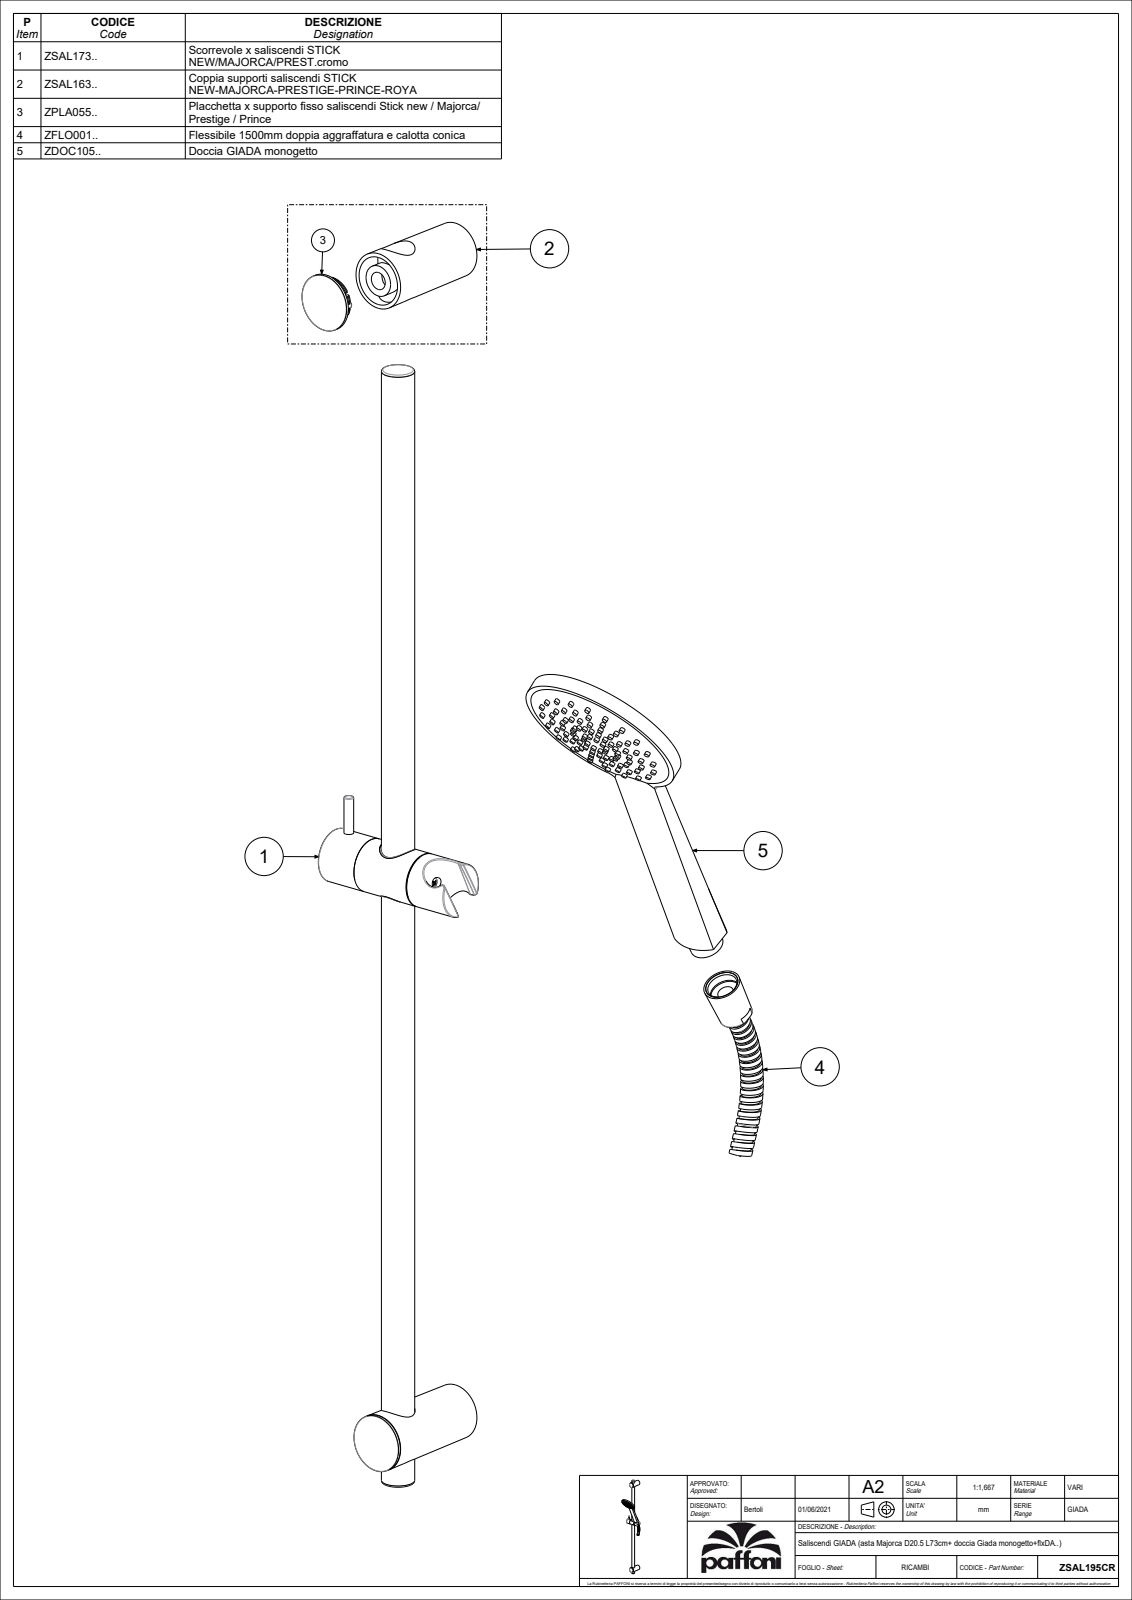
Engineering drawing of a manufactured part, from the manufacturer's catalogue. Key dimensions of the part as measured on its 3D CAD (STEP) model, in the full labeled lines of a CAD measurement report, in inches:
Part name (STEP PRODUCT): ZSAL195CR
STEP written by: CREO PARAMETRIC BY PTC INC, 2020044 (CONFIG_CONTROL_DESIGN)
Units: inches
Bodies: 5 solids, 769 faces (161 planar, 347 cylindrical, 261 other)
Overall size (bounding box): 28.898 × 7.874 × 5.693
Volume: 36.75 in³ · Surface area: 277.4 in²
Round holes (diameter × count): ⌀1.22 ×3, ⌀0.213 ×2, ⌀0.441 ×2, ⌀0.886 ×2, ⌀0.15 ×1, ⌀0.315 ×1, ⌀0.433 ×1, ⌀0.551 ×1, ⌀0.709 ×1, ⌀0.787 ×1, ⌀0.819 ×1, ⌀0.827 ×1
Round bosses / shafts (diameter × count): ⌀0.118 ×90, ⌀1.437 ×2, ⌀1.378 ×2, ⌀0.882 ×2, ⌀0.472 ×2, ⌀4.134 ×1, ⌀1.339 ×1, ⌀1.28 ×1
Partial cylindrical surfaces — rounded edges, fillets, slot ends (radius × count): R0.059 ×9, R0.024 ×8, R0.02 ×6, R0.012 ×4, R0.506 ×2, R0.557 ×2, R0.161 ×1, R0.492 ×1
Main face-to-face distances: 0.043, 14.43, 14.473, 14.386, 0.079, 2.685, 2.764, 0.039, 0.059, 2.913
Hole centre spacings: 22.441
